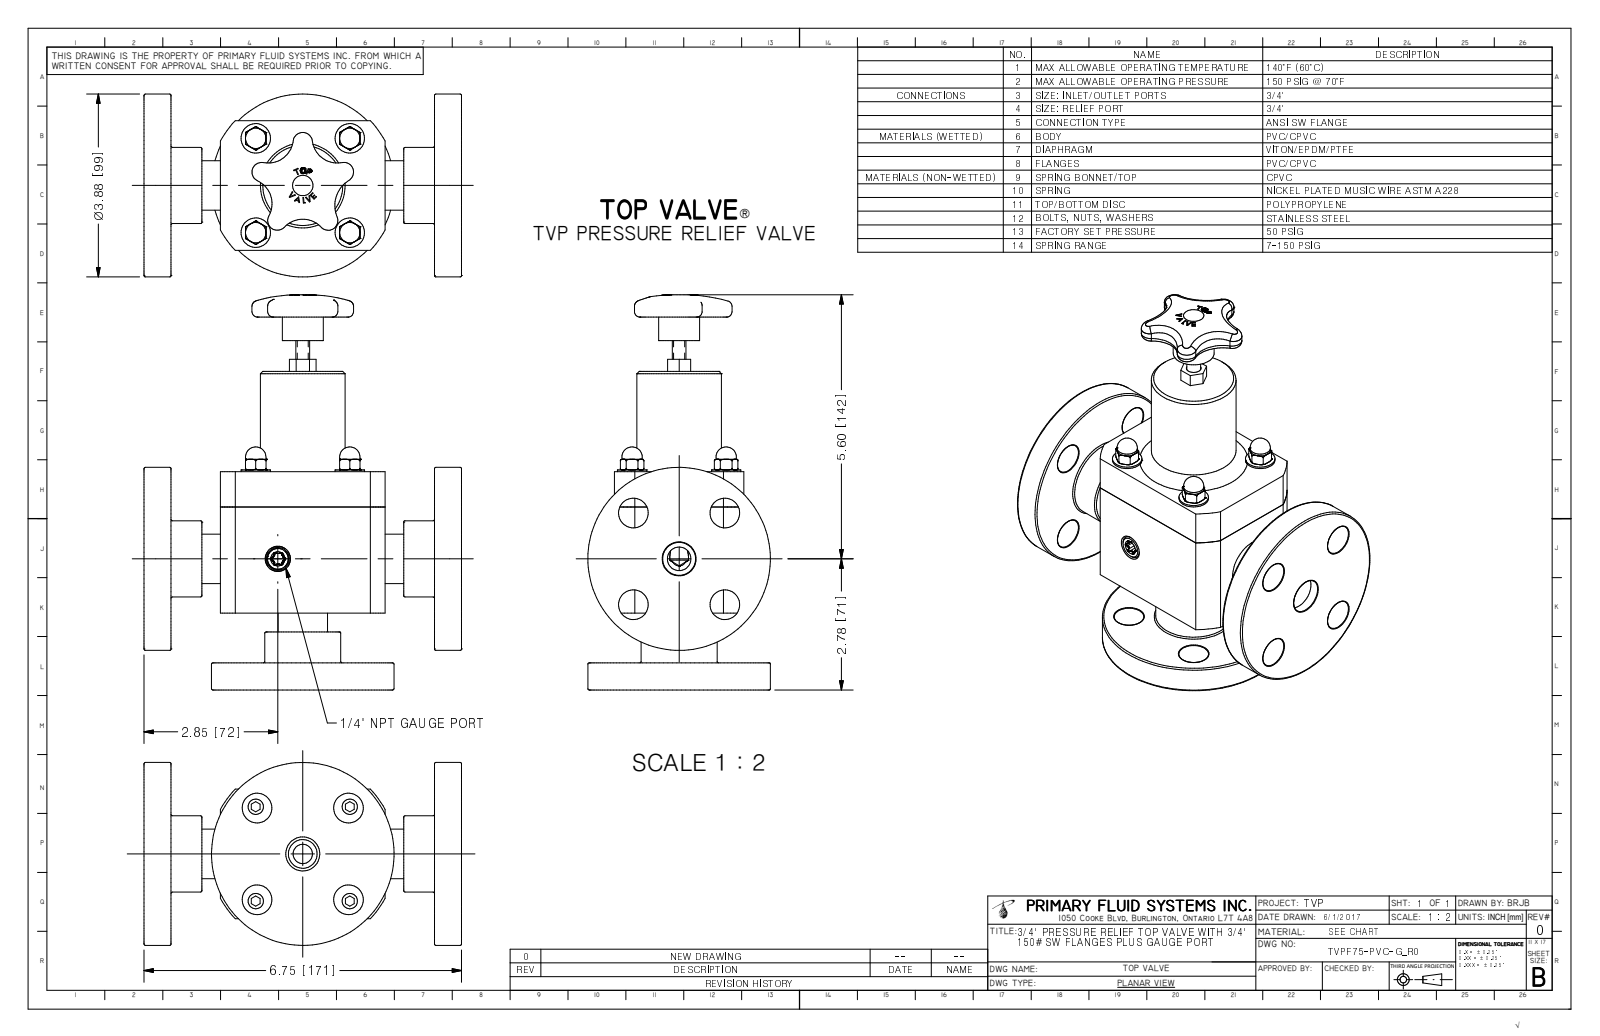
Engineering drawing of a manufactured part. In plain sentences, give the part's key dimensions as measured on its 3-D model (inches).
The part is named "TVPF75-PVC-G_R0". Its 3-D file was written by "Autodesk Inventor 2009 (AUTOMOTIVE_DESIGN)". It is 1 solid with 438 faces: 168 planar, 74 cylindrical and 196 other. Overall it measures 8.38 by 6.75 by 3.88 inches. Its volume is 55.73 cubic inches and its surface area 219.8 square inches. Round holes: 8 of diameter 0.63, 4 of diameter 0.175, 2 of diameter 0.722, 2 of diameter 0.742, 1 of diameter 2.4. Round bosses or shafts: 4 of diameter 0.625, 4 of diameter 0.433, 2 of diameter 3.88, 2 of diameter 1.616, 2 of diameter 1.05, 1 of diameter 2.375, 1 of diameter 1.8, 1 of diameter 0.87. Partial cylindrical surfaces (rounded edges, fillets, slot ends): 6 of radius 0.027, 5 of radius 0.085, 5 of radius 0.205, 4 of radius 0.536, 4 of radius 0.656, 1 of radius 0.625, 1 of radius 0.745, 1 of radius 1.988. The main face-to-face distances are 0.575, 6.175, 5.125, 6.75, 1.05, 1.625, 4.55, 2.75, 1.63, 0.575. The hole center spacings are 1.375, 1.945, 1.972, 0.039, 1.414, 2, 2.75, 2.789.
